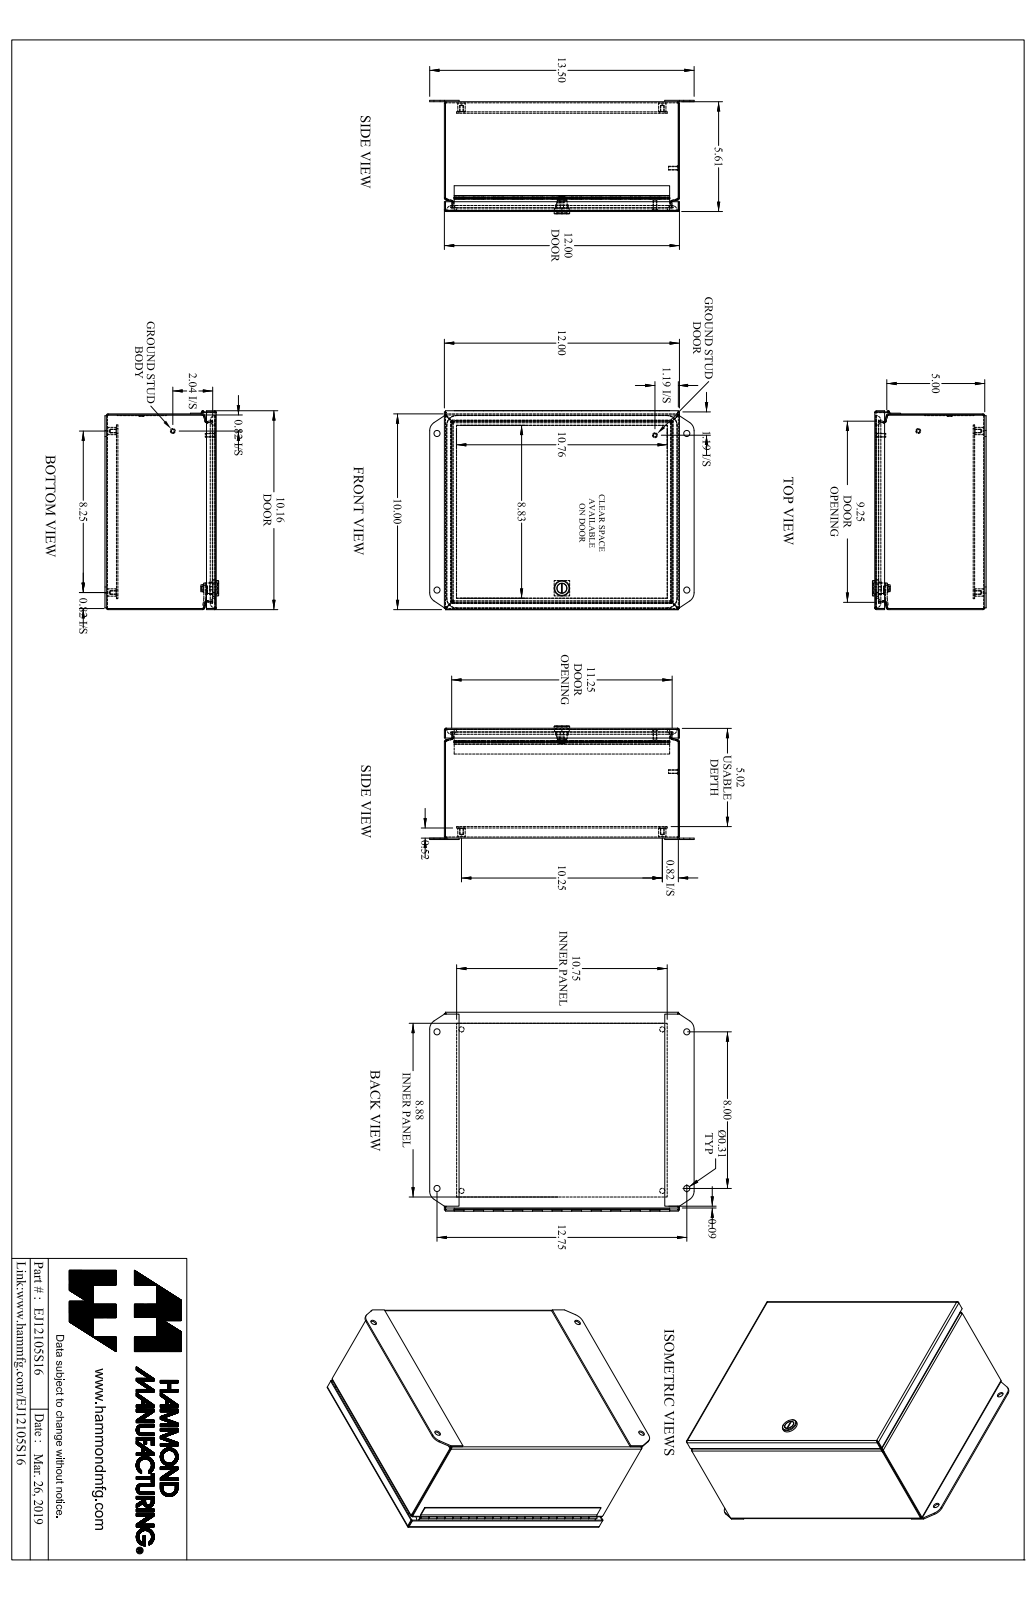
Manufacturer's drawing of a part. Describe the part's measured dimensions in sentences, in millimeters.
The part is named "EJ12105S16_Default". Its 3-D file was written by "SolidWorks 2019 (CONFIG_CONTROL_DESIGN)". It is 16 solids with 628 faces: 326 planar, 222 cylindrical and 80 other. Overall it measures 342.9 by 258.2 by 147.4 millimeters. Its volume is 697 900 cubic millimeters and its surface area 905 800 square millimeters. Round holes: 4 of diameter 4, 4 of diameter 6.7, 4 of diameter 8, 1 of diameter 1.3, 1 of diameter 13.1. Round bosses or shafts: 4 of diameter 9.5, 2 of diameter 6.4, 2 of diameter 4.8, 1 of diameter 20, 1 of diameter 13.6, 1 of diameter 12.6, 1 of diameter 11, 1 of diameter 2.5. Partial cylindrical surfaces (rounded edges, fillets, slot ends): 16 of radius 0.7, 16 of radius 2.2, 12 of radius 7.1, 4 of radius 6.4, 4 of radius 12.7, 4 of radius 12.7, 2 of radius 1.5, 1 of radius 0.8. The main face-to-face distances are 1.4, 141.1, 1.8, 15, 142.5, 139.6, 252.6, 303.4, 129.4, 127.9. The hole center spacings are 31.9, 292.1, 357.7, 260.4, 208.8, 334.2, 130.3, 162.
